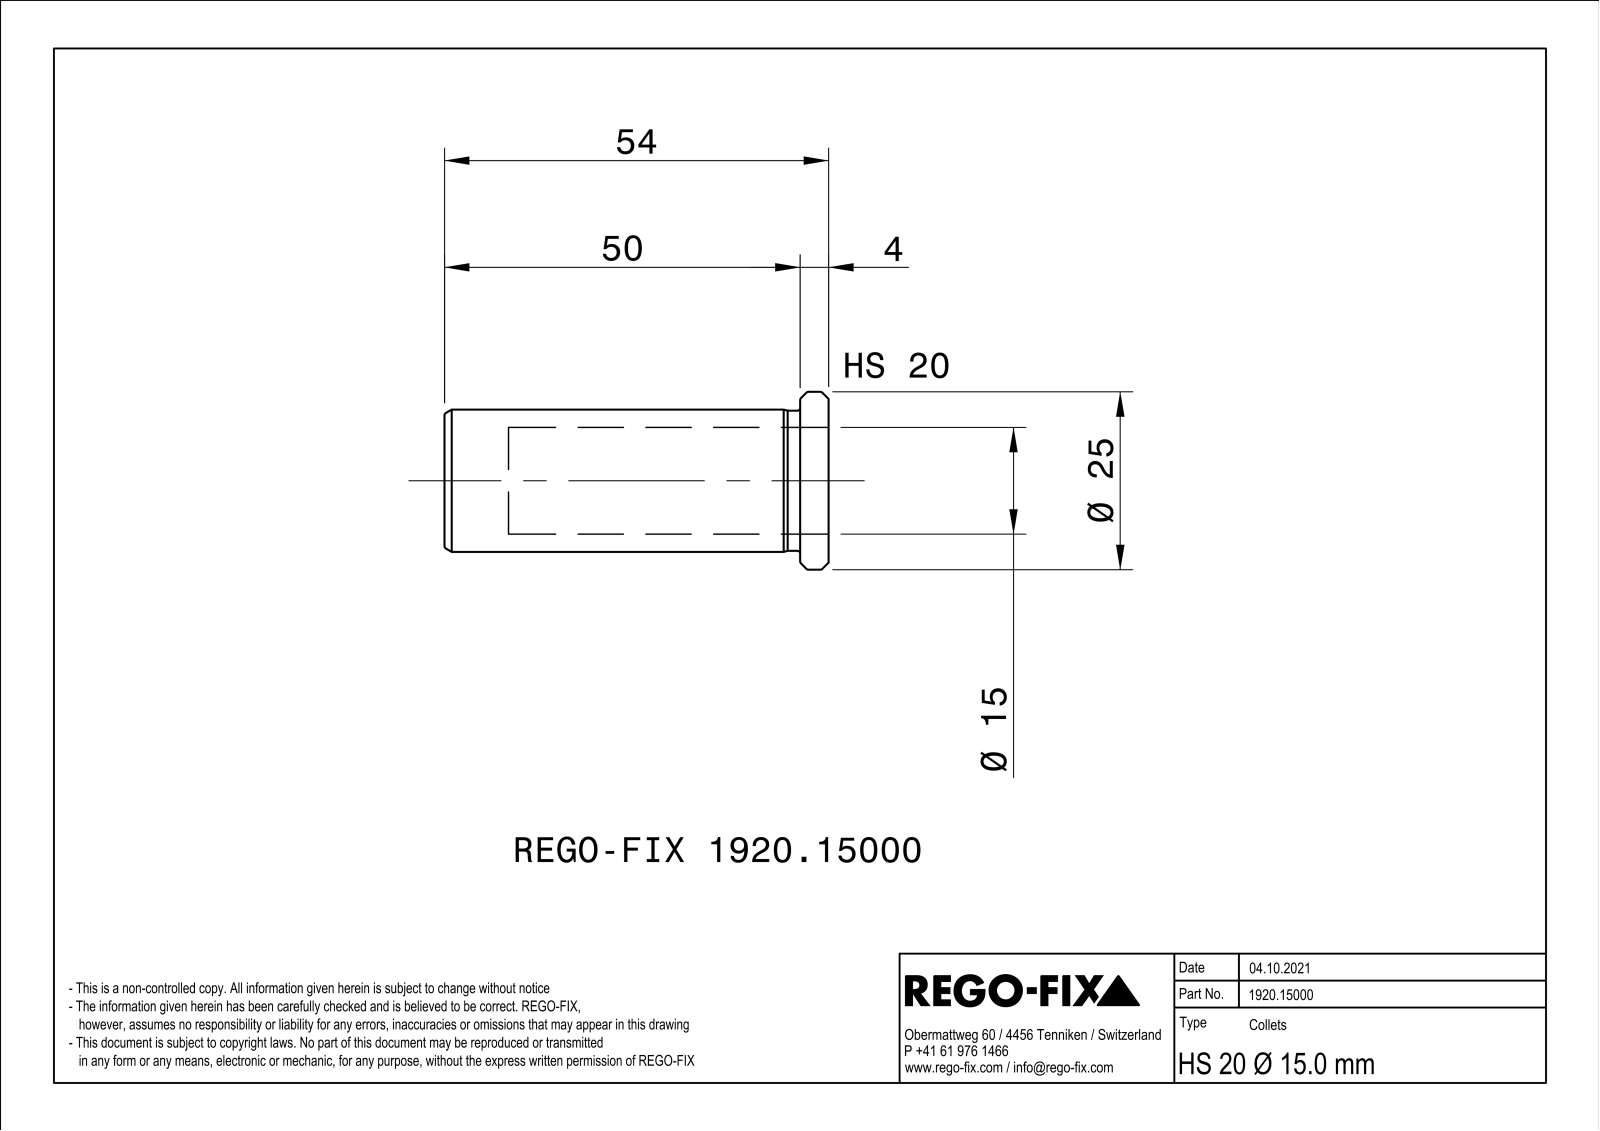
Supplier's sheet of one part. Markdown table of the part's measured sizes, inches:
| quantity | value |
| --- | --- |
| part name | NOCUT |
| STEP written by | SIEMENS PLM Software Solid Edge ST10 (AUTOMOTIVE_DESIGN) |
| units | inches |
| bodies | 1 solid, 71 faces (22 planar, 11 cylindrical, 38 other) |
| overall size | 2.126 × 0.983 × 0.983 |
| volume | 0.449 in³ |
| surface area | 10.81 in² |
| round holes (diameter × count) | 0.591 × 1, 0.65 × 1 |
| round bosses / shafts (diameter × count) | 0.984 × 1, 0.787 × 1, 0.776 × 1 |
| main face-to-face distances | 0.039, 0.157, 2.126, 1.969 |
